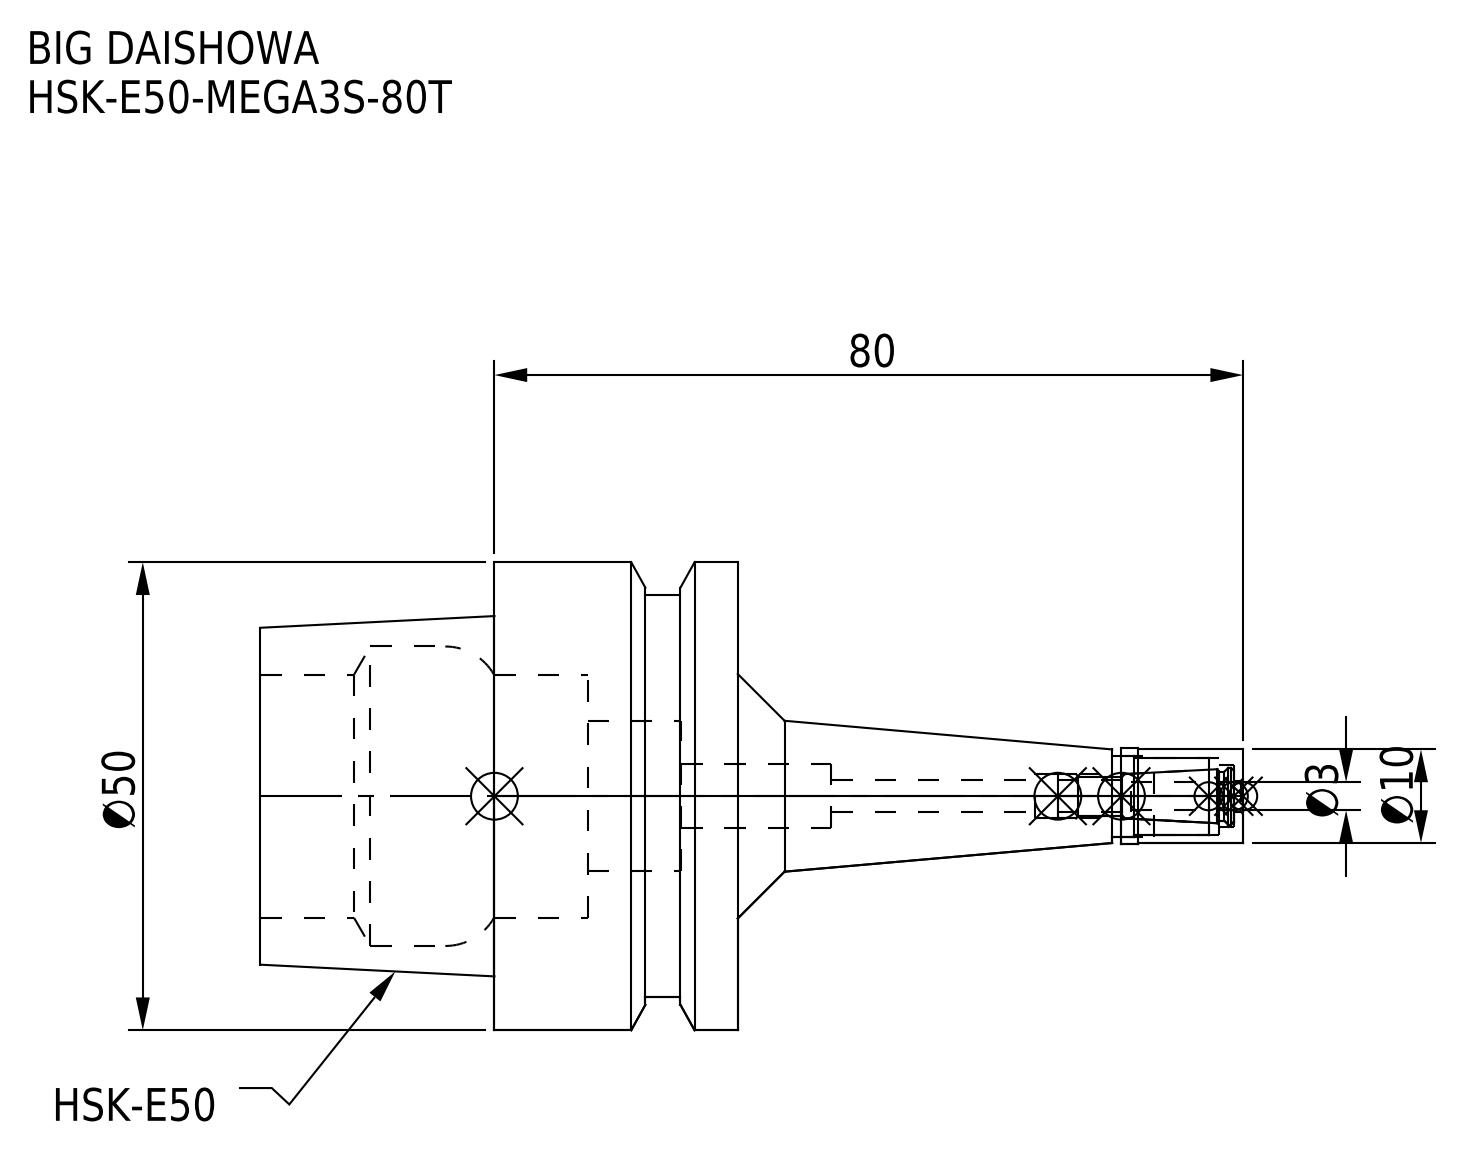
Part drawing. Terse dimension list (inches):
name: MGN3S_1.stp; HSK-E50-MEGA3S-80T; DXF_TEMP_ASSY_ASM_4_ASM.stp; HSK-E50-MEGA3S-80T-030-FreeParts (+3 more)
written by: SolidWorks 2019 (CONFIG_CONTROL_DESIGN)
unit: in
bodies: 2 solids, 74 faces (18 planar, 38 cylindrical, 18 other)
size: 4.134 × 1.969 × 1.969
volume: 3.55 in³; area: 28.92 in²
holes: 1× ⌀0.13, 1× ⌀0.134, 1× ⌀0.185, 1× ⌀0.26, 1× ⌀0.268, 1× ⌀0.323, 1× ⌀0.343, 1× ⌀0.63, 1× ⌀1.024, 1× ⌀1.26
bosses: 1× ⌀1.969, 1× ⌀1.693, 1× ⌀0.406, 1× ⌀0.394
face distances: 1.024, 2.008, 0.984, 0.632, 0.392, 1.376, 0.394, 0.238, 0.785, 1.77
